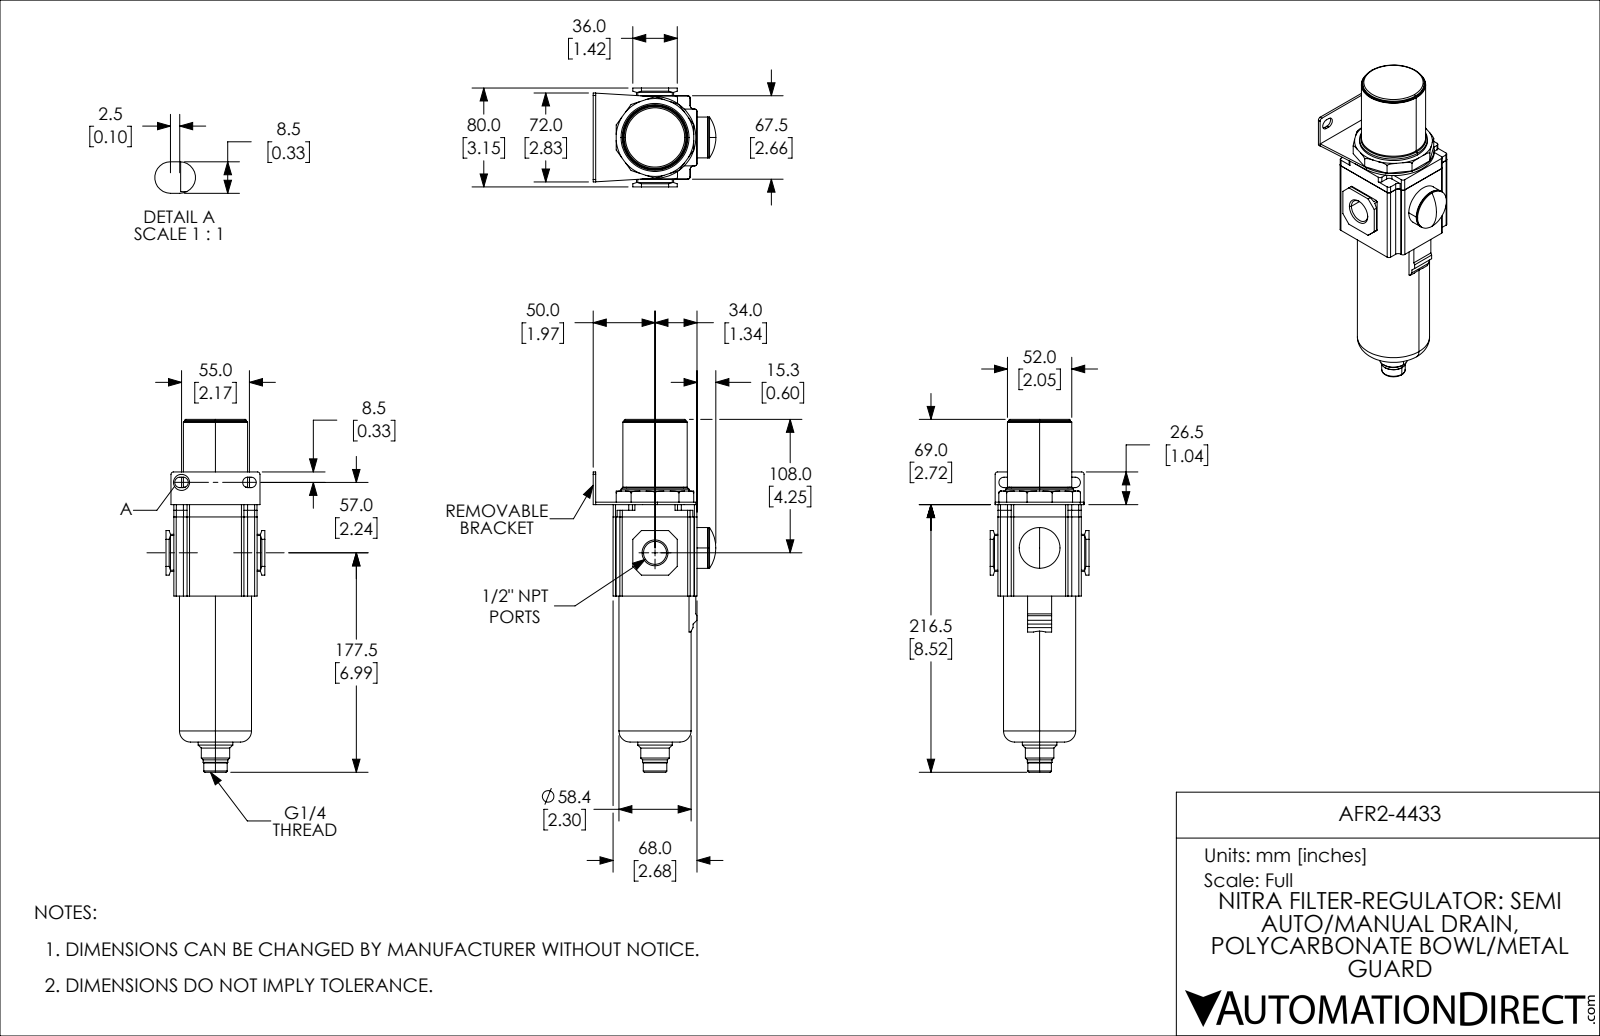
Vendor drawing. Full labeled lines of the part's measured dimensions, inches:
Part name (STEP PRODUCT): AFR2-4433
STEP written by: SolidWorks 2019 (CONFIG_CONTROL_DESIGN)
Units: inches
Bodies: 1 solid, 222 faces (119 planar, 67 cylindrical, 36 other)
Overall size (bounding box): 11.24 × 3.909 × 3.15
Volume: 50.17 in³ · Surface area: 117.8 in²
Round holes (diameter × count): ⌀0.451 ×1, ⌀0.733 ×1
Round bosses / shafts (diameter × count): ⌀2.299 ×1, ⌀2.165 ×1, ⌀2.047 ×1, ⌀1.969 ×1, ⌀1.807 ×1, ⌀1.299 ×1, ⌀1.102 ×1, ⌀0.906 ×1
Partial cylindrical surfaces — rounded edges, fillets, slot ends (radius × count): R0.079 ×22, R0.118 ×12, R0.167 ×4, R1.299 ×1
Main face-to-face distances: 0.079, 2.657, 2.638, 2.677, 0.63, 2.717, 3.307, 0.246, 2.904, 2.992
